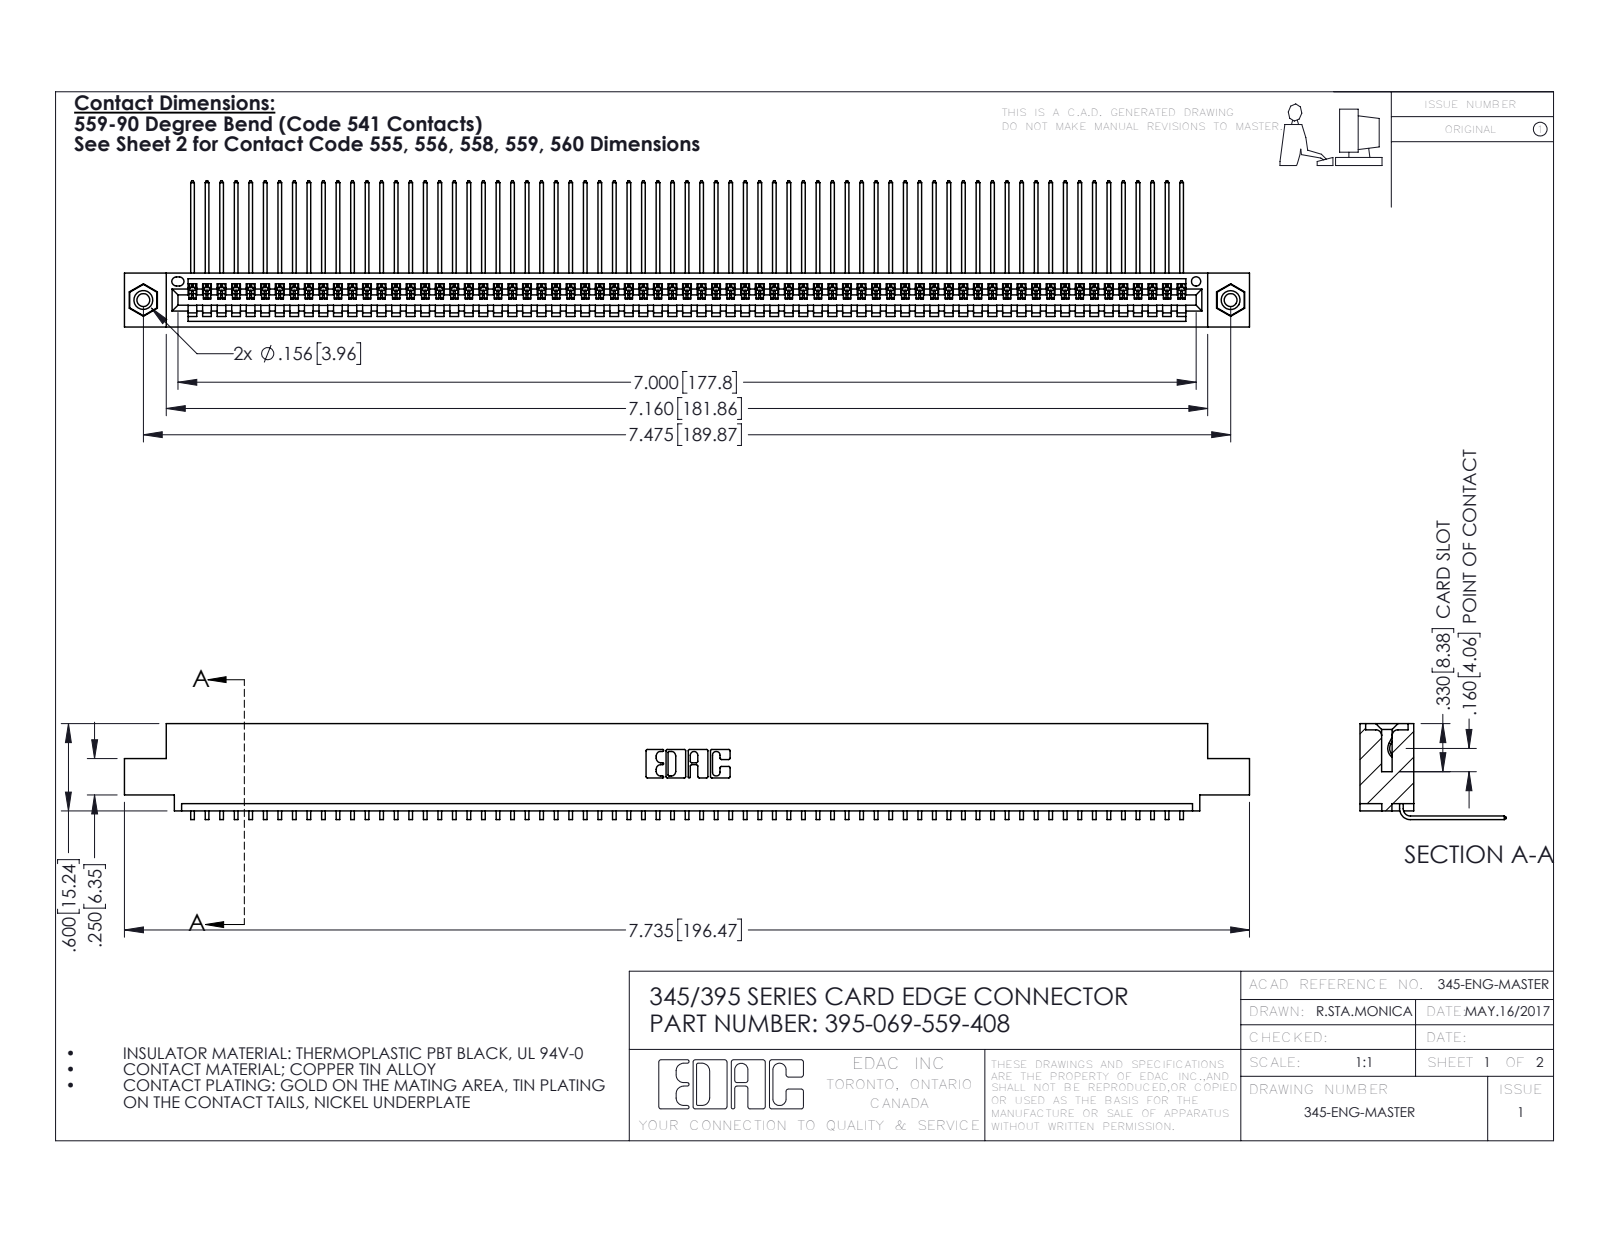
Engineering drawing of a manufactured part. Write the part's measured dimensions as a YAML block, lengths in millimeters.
part_name: "345 Part_0.110 Offset - 0.156 Dia-TI; 345-292-001_558 559 Tail - 1; 345-250-001_345-250-003-102; 395-069-559-408"
step_written_by: "SolidWorks 2016 (CONFIG_CONTROL_DESIGN)"
units: millimeters
bodies: {solids: 72, faces: 4330, planar: 3014, cylindrical: 1300, other: 16}
overall_size: [196.5, 25.5, 16.7]
volume: 19030
surface_area: 27110
round_holes:
  - {diameter: 2.3, count: 2}
  - {diameter: 3.2, count: 2}
  - {diameter: 4, count: 2}
  - {diameter: 1.6, count: 1}
round_bosses_or_shafts:
  - {diameter: 3.9, count: 2}
partial_cylinders:
  - {radius: 0.2, count: 138}
  - {radius: 0.3, count: 22}
  - {radius: 0.2, count: 6}
  - {radius: 0.8, count: 6}
  - {radius: 0.7, count: 3}
  - {radius: 0.8, count: 2}
  - {radius: 1, count: 2}
  - {radius: 0.4, count: 1}
face_to_face_distances: [1.8, 7.6, 9.4, 5.1, 2.5, 6.9, 0.6, 5.7, 3.8, 1.8]
hole_center_spacings: [6.9, 183.9, 189.9]
